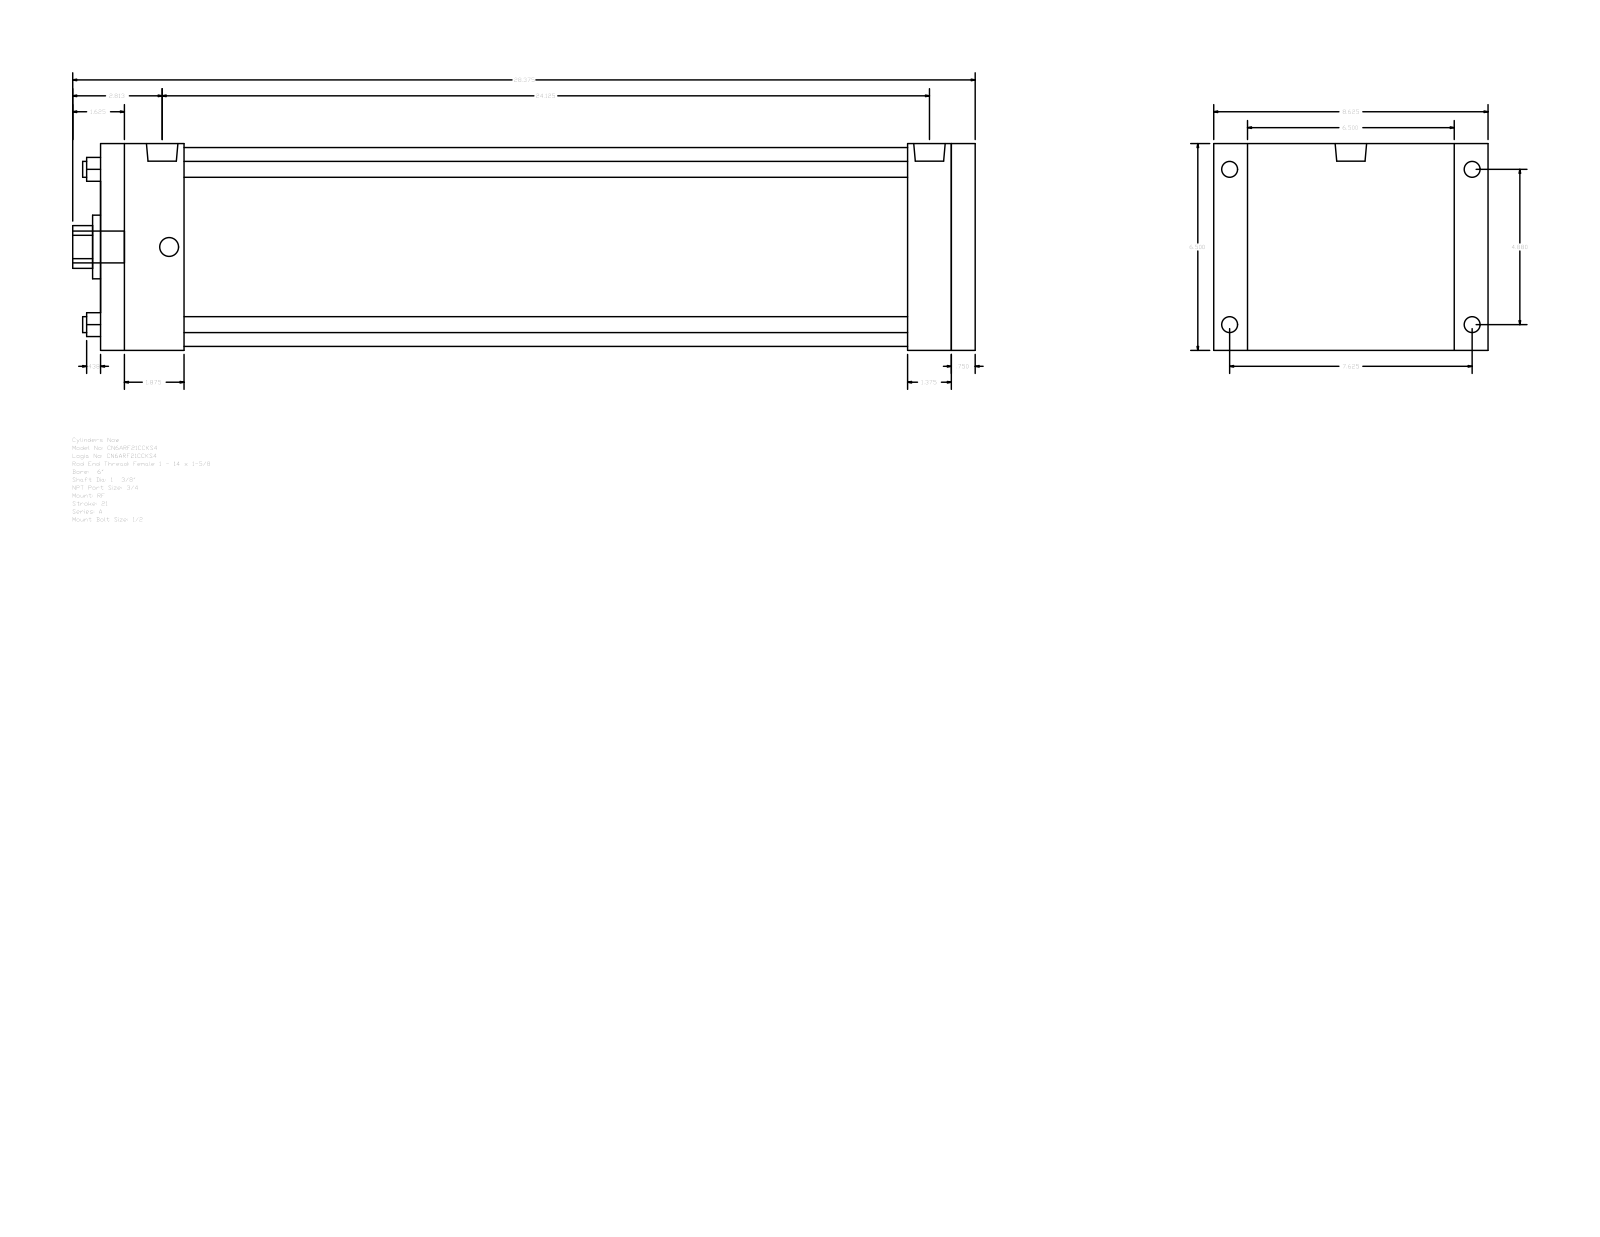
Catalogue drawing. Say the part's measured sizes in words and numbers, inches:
The part is named "A_RF__0600_1.375". Its 3-D file was written by "GSSL Pune (CONFIG_CONTROL_DESIGN)". It is 0 solids with 92 faces: 64 planar, 28 cylindrical and 0 other. Overall it measures 28.375 by 8.625 by 6.5 inches. Round holes: 4 of diameter 0.5, 1 of diameter 1.375, 1 of diameter 2, 1 of diameter 6.25. Round bosses or shafts: 4 of diameter 0.594, 4 of diameter 0.5, 2 of diameter 0.989, 1 of diameter 1. Partial cylindrical surfaces (rounded edges, fillets, slot ends): 1 of radius 0.672. The main face-to-face distances are 6.5, 27.5, 26.75, 0.75, 2.625, 24.125, 24.875, 25.375, 22.75, 1.375. The hole center spacings are 3.451, 4.88, 6.902.
